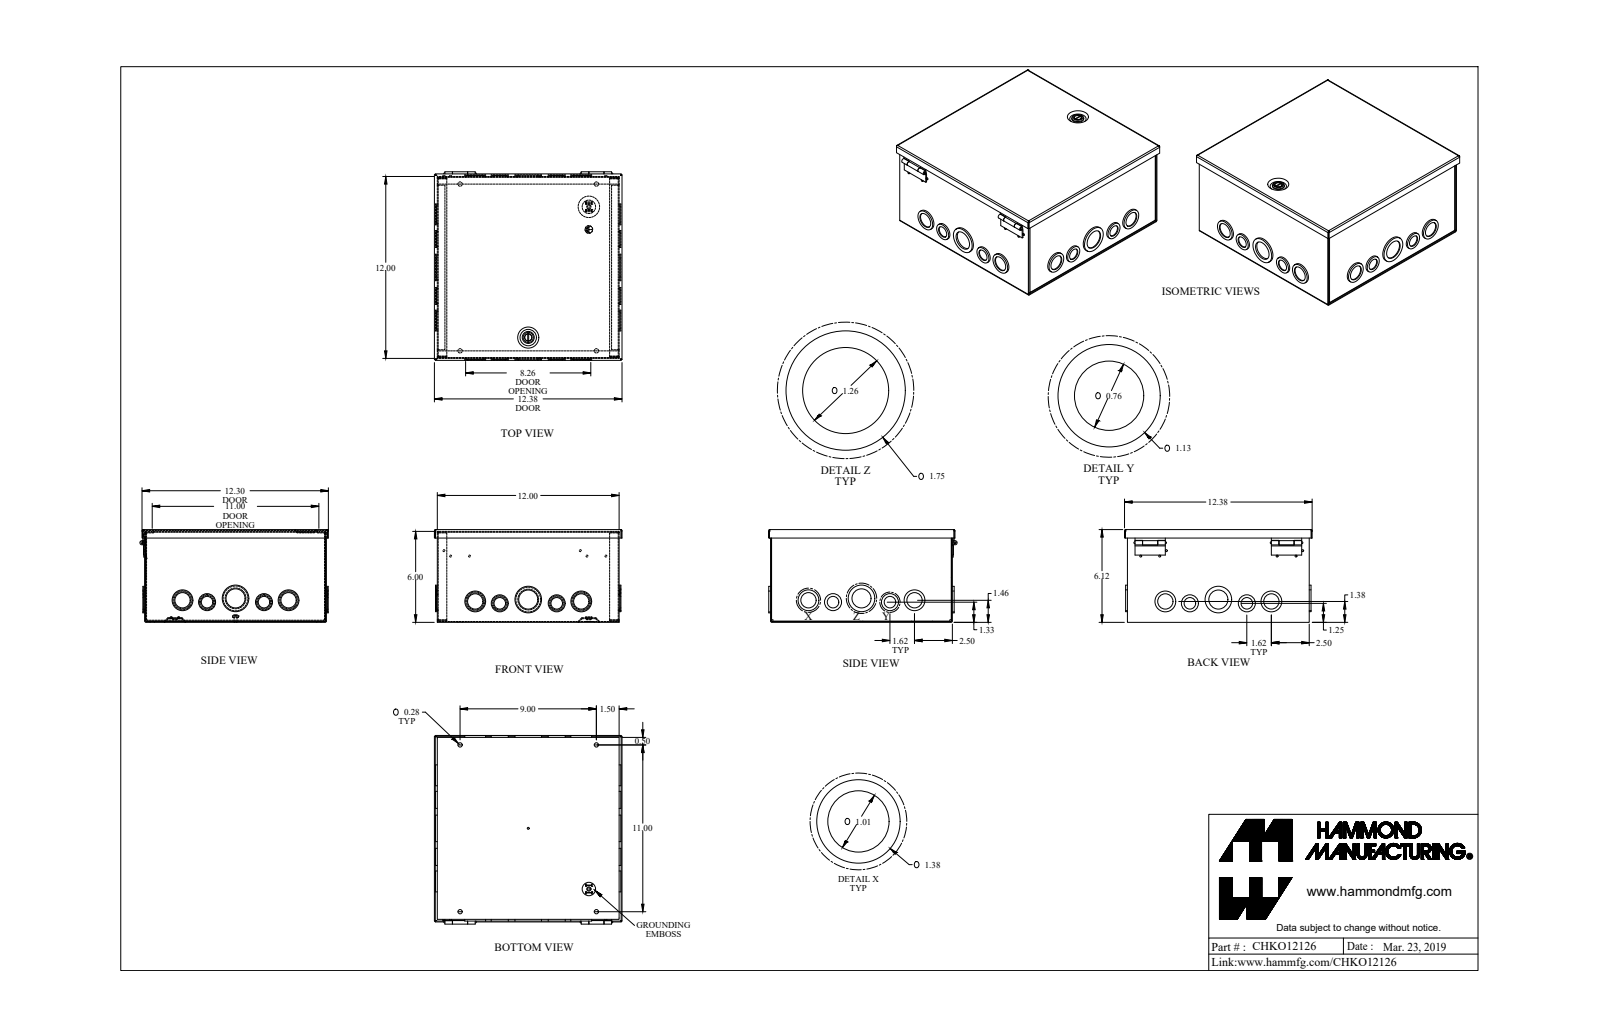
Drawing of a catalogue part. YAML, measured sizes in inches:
part_name: "CHKO12126_Default"
step_written_by: "SolidWorks 2019 (CONFIG_CONTROL_DESIGN)"
units: inches
bodies: {solids: 12, faces: 727, planar: 352, cylindrical: 332, other: 43}
overall_size: [12.443, 12.38, 6.118]
volume: 38.61
surface_area: 1361
round_holes:
  - {diameter: 1.011, count: 8}
  - {diameter: 1.261, count: 6}
  - {diameter: 0.281, count: 4}
  - {diameter: 0.761, count: 4}
  - {diameter: 1.636, count: 2}
  - {diameter: 0.125, count: 1}
  - {diameter: 0.17, count: 1}
  - {diameter: 0.319, count: 1}
  - {diameter: 0.476, count: 1}
  - {diameter: 0.5, count: 1}
round_bosses_or_shafts:
  - {diameter: 0.131, count: 8}
  - {diameter: 1.125, count: 6}
  - {diameter: 1.375, count: 5}
  - {diameter: 0.875, count: 4}
  - {diameter: 0.875, count: 4}
  - {diameter: 1.375, count: 3}
  - {diameter: 1.75, count: 2}
  - {diameter: 1.125, count: 2}
partial_cylinders:
  - {radius: 0.029, count: 16}
  - {radius: 0.086, count: 16}
  - {radius: 0.057, count: 8}
  - {radius: 0.012, count: 4}
  - {radius: 0.1, count: 4}
  - {radius: 0.036, count: 2}
  - {radius: 0.079, count: 2}
  - {radius: 0.25, count: 2}
face_to_face_distances: [0.057, 6.061, 11.943, 12, 6.118, 6.004, 11.886, 5.943, 0.118, 0.08]
hole_center_spacings: [1.625, 1.896, 3.502, 5.381, 3.76, 7, 9, 11]
